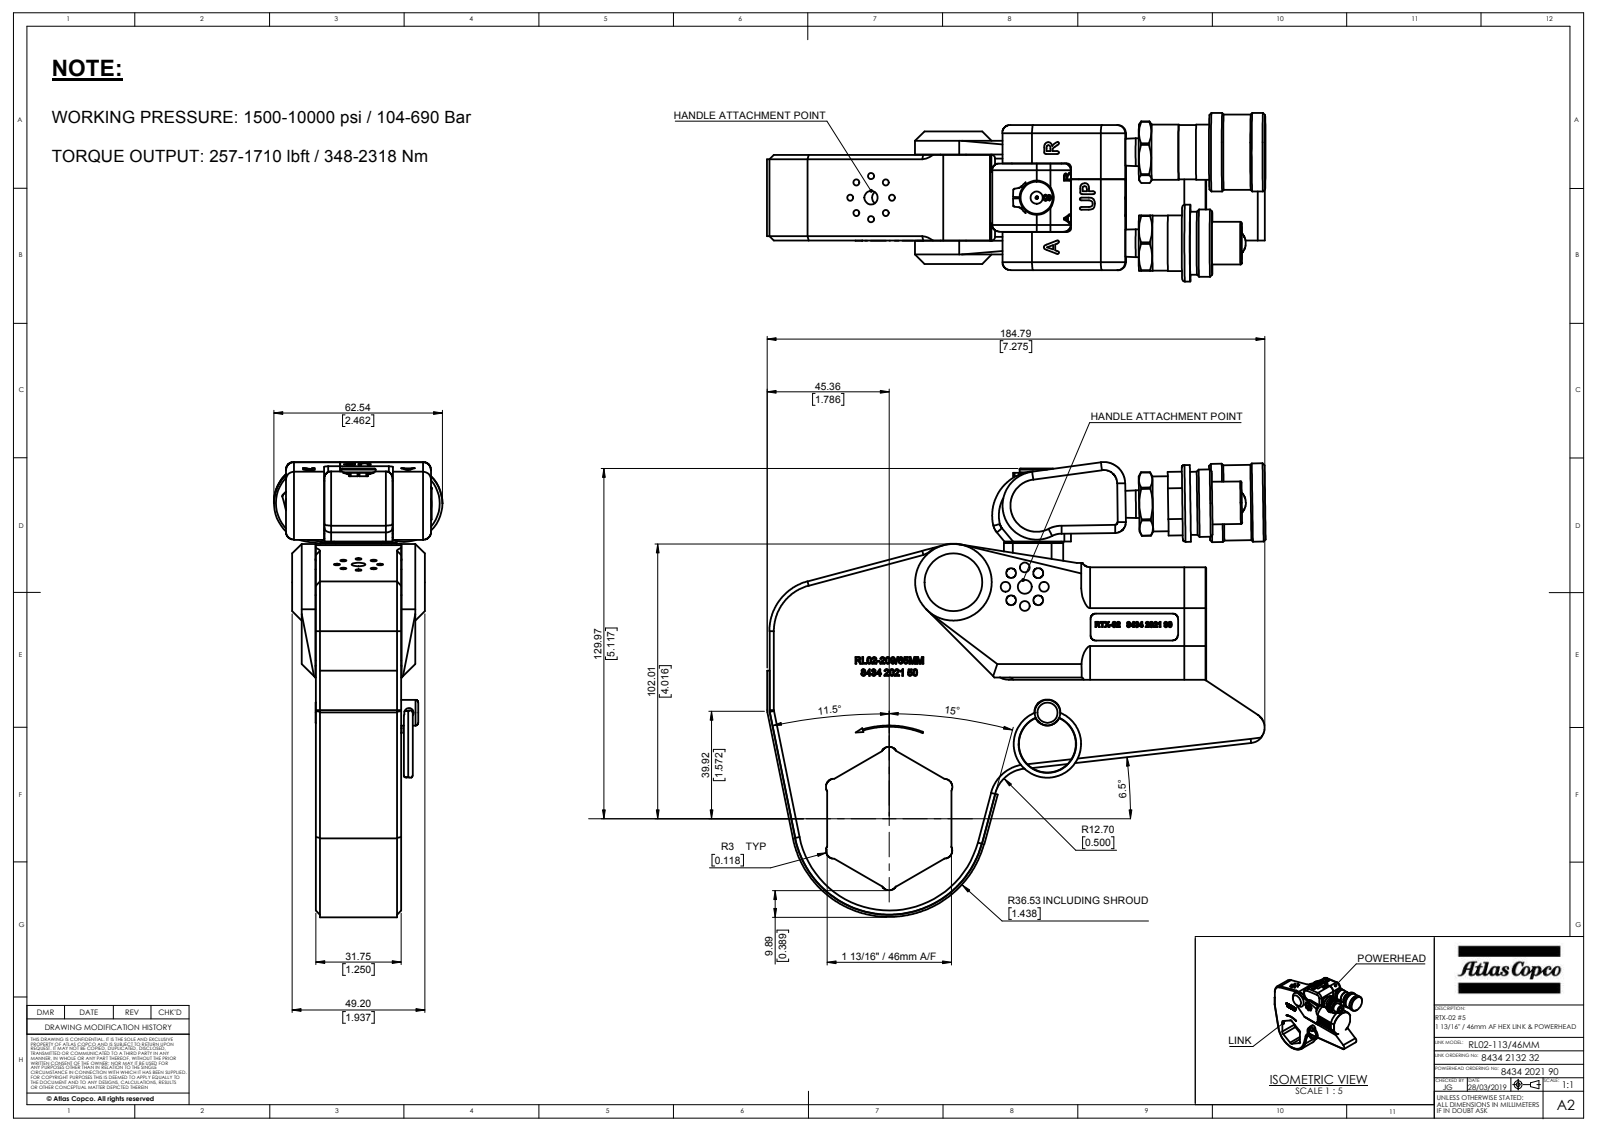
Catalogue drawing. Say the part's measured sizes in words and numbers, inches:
The part is named "RTX-02 with RL02#05 [1-13_16in-46mm]". Its 3-D file was written by "SolidWorks 2017 (CONFIG_CONTROL_DESIGN)". It is 5 solids with 1544 faces: 674 planar, 227 cylindrical and 643 other. Overall it measures 7.287 by 6.651 by 2.462 inches. Its volume is 35.69 cubic inches and its surface area 163.6 square inches. Round holes: 2 of diameter 0.137, 1 of diameter 0.138, 1 of diameter 0.201, 1 of diameter 0.205, 1 of diameter 0.378, 1 of diameter 0.561, 1 of diameter 0.571, 1 of diameter 0.669, 1 of diameter 0.724. Round bosses or shafts: 4 of diameter 0.164, 2 of diameter 0.805, 2 of diameter 0.406, 1 of diameter 1.75, 1 of diameter 1.144, 1 of diameter 1.122, 1 of diameter 1.1, 1 of diameter 0.984. Partial cylindrical surfaces (rounded edges, fillets, slot ends): 9 of radius 0.059, 7 of radius 0.098, 6 of radius 0.118, 6 of radius 0.118, 6 of radius 0.25, 5 of radius 0.079, 4 of radius 0.016, 4 of radius 0.15. The main face-to-face distances are 1.25, 0.205, 1.455, 1.817, 0.2, 1.46, 1.255, 1.66, 0.23, 0.43. The hole center spacings are 0.931, 1.199, 1.87, 3.03.
